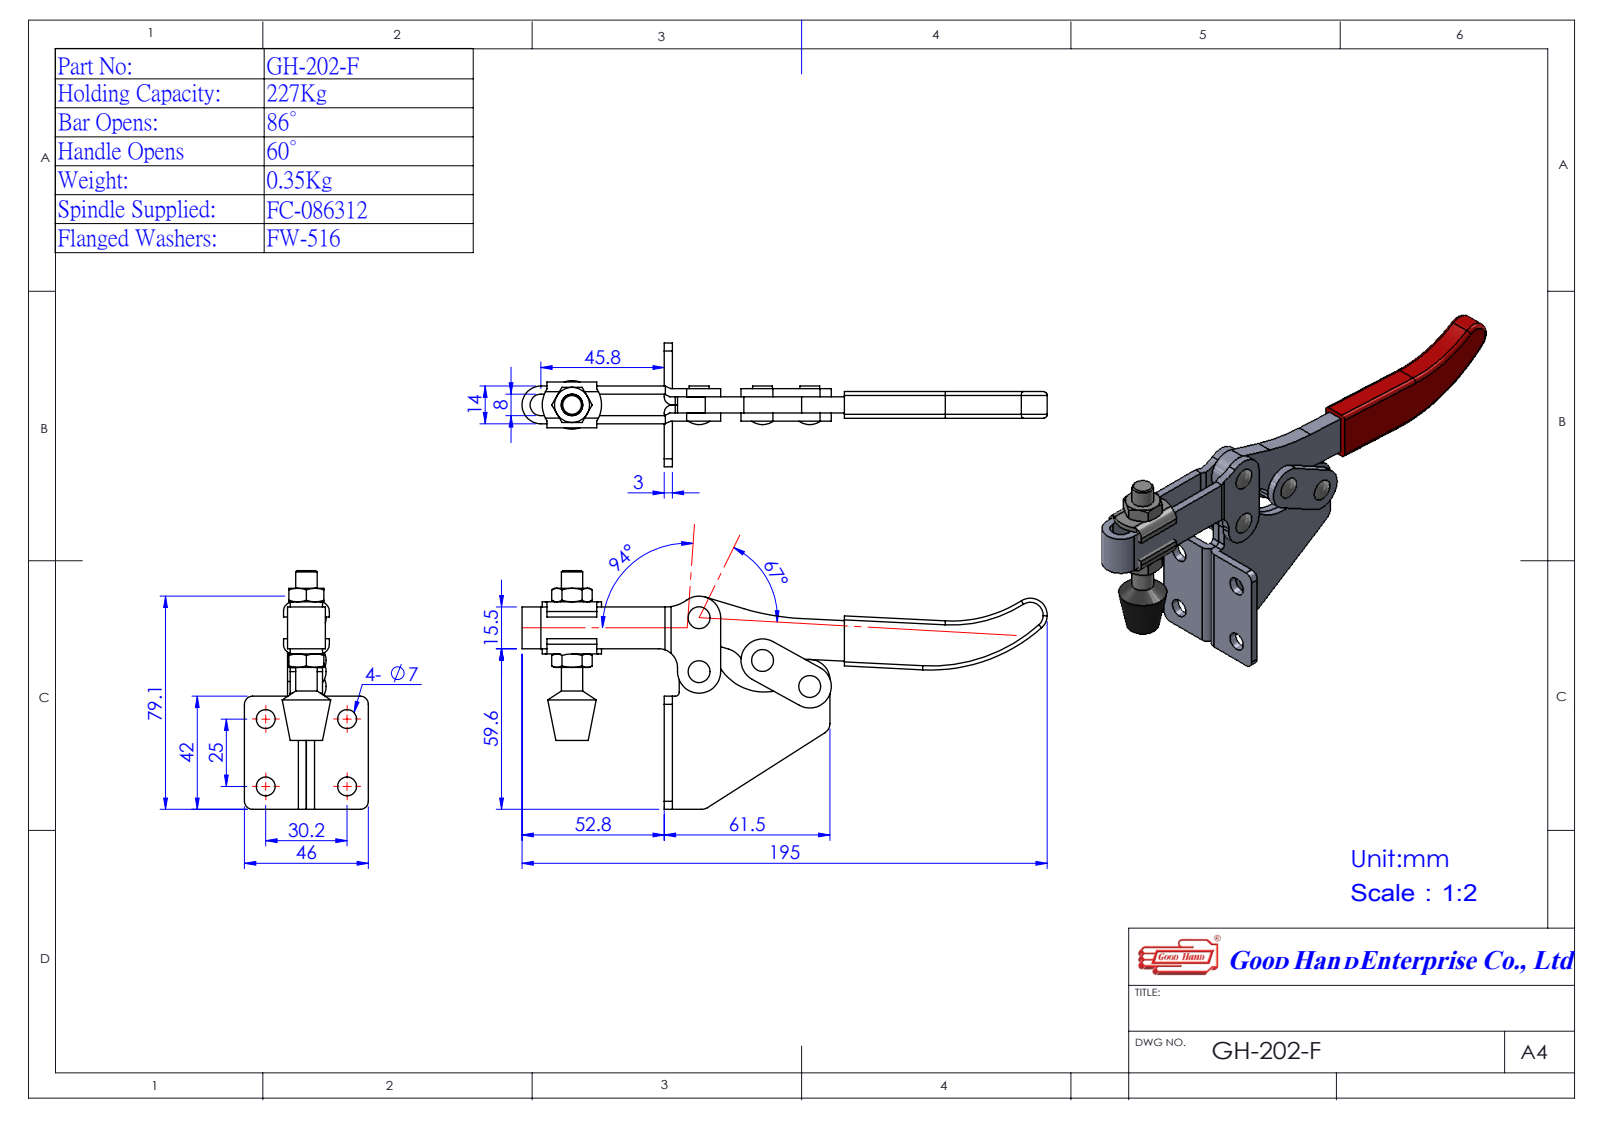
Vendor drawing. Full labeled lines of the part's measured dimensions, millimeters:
Part name (STEP PRODUCT): Group5^GH-202-F(簡化)-1; 1203F01-1^GH-202-F(簡化)-1; GH-202-F(簡化)-1; Group1^GH-202-F(簡化) (+2 more)
STEP written by: SolidWorks 2016 (AUTOMOTIVE_DESIGN)
Units: millimetres
Bodies: 5 solids, 254 faces (107 planar, 109 cylindrical, 38 other)
Overall size (bounding box): 195 × 88.6 × 46
Volume: 57 907 mm³ · Surface area: 31 625 mm²
Round holes (diameter × count): ⌀5 ×4, ⌀7 ×4, ⌀6.33 ×1
Round bosses / shafts (diameter × count): ⌀7.35 ×4, ⌀7.93 ×1, ⌀5 ×1
Partial cylindrical surfaces — rounded edges, fillets, slot ends (radius × count): R3 ×7, R8 ×6, R1.2 ×4, R3.6 ×4, R4 ×3, R7 ×2, R11.04 ×2, R1.5 ×1
Main face-to-face distances: 1, 2, 3, 10, 6, 8, 11, 9, 12, 13
Hole centre spacings: 25, 30.2, 39.21, 19.93, 20, 23.92, 28.4, 41.37
